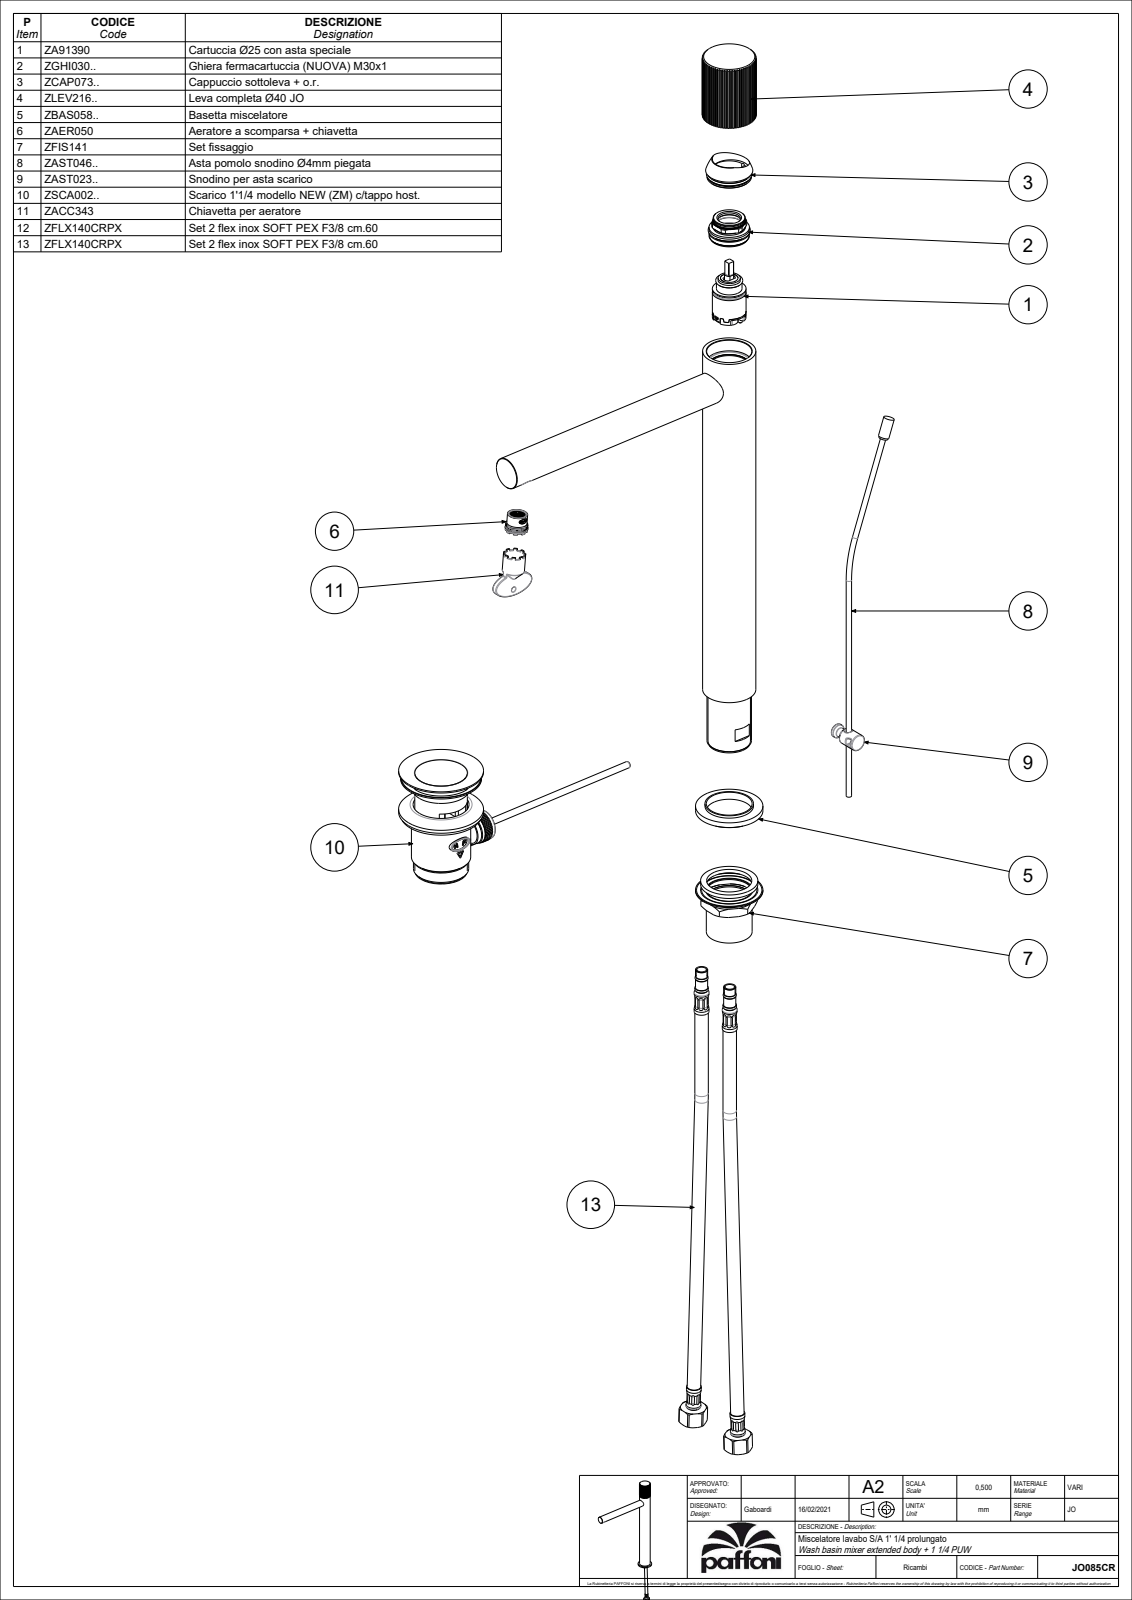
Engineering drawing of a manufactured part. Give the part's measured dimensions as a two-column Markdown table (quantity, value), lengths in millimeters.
| quantity | value |
| --- | --- |
| part name | JO085CR |
| STEP written by | CREO PARAMETRIC BY PTC INC, 2020044 (CONFIG_CONTROL_DESIGN) |
| units | millimeters |
| bodies | 2 solids, 3112 faces (2067 planar, 690 cylindrical, 355 other) |
| overall size | 346.85 × 251.38 × 50 |
| volume | 225 136 mm³ |
| surface area | 154 203 mm² |
| round holes (diameter × count) | 6.5 × 4, 5 × 3, 7 × 3, 3.2 × 2, 5.5 × 2, 9.4 × 2, 11 × 2, 3 × 1, 4.2 × 1, 8 × 1, 12.15 × 1, 12.45 × 1 |
| round bosses / shafts (diameter × count) | 10 × 4, 4 × 3, 0.9 × 3, 11 × 2, 9 × 2, 8 × 2, 50 × 1, 43 × 1 |
| partial cylindrical surfaces (radius × count) | 0.12 × 51, 3 × 28, 0.5 × 12, 0.2 × 8, 0.6 × 5, 1 × 5, 2 × 4, 3.5 × 3 |
| main face-to-face distances | 27.58, 2, 4, 344.5, 27.59, 340.5, 50.5, 6.5, 243.5, 239.5 |
| hole center spacings | 1.5, 6.72, 7.85, 8.92, 8.94, 9.33, 11, 15.46 |
